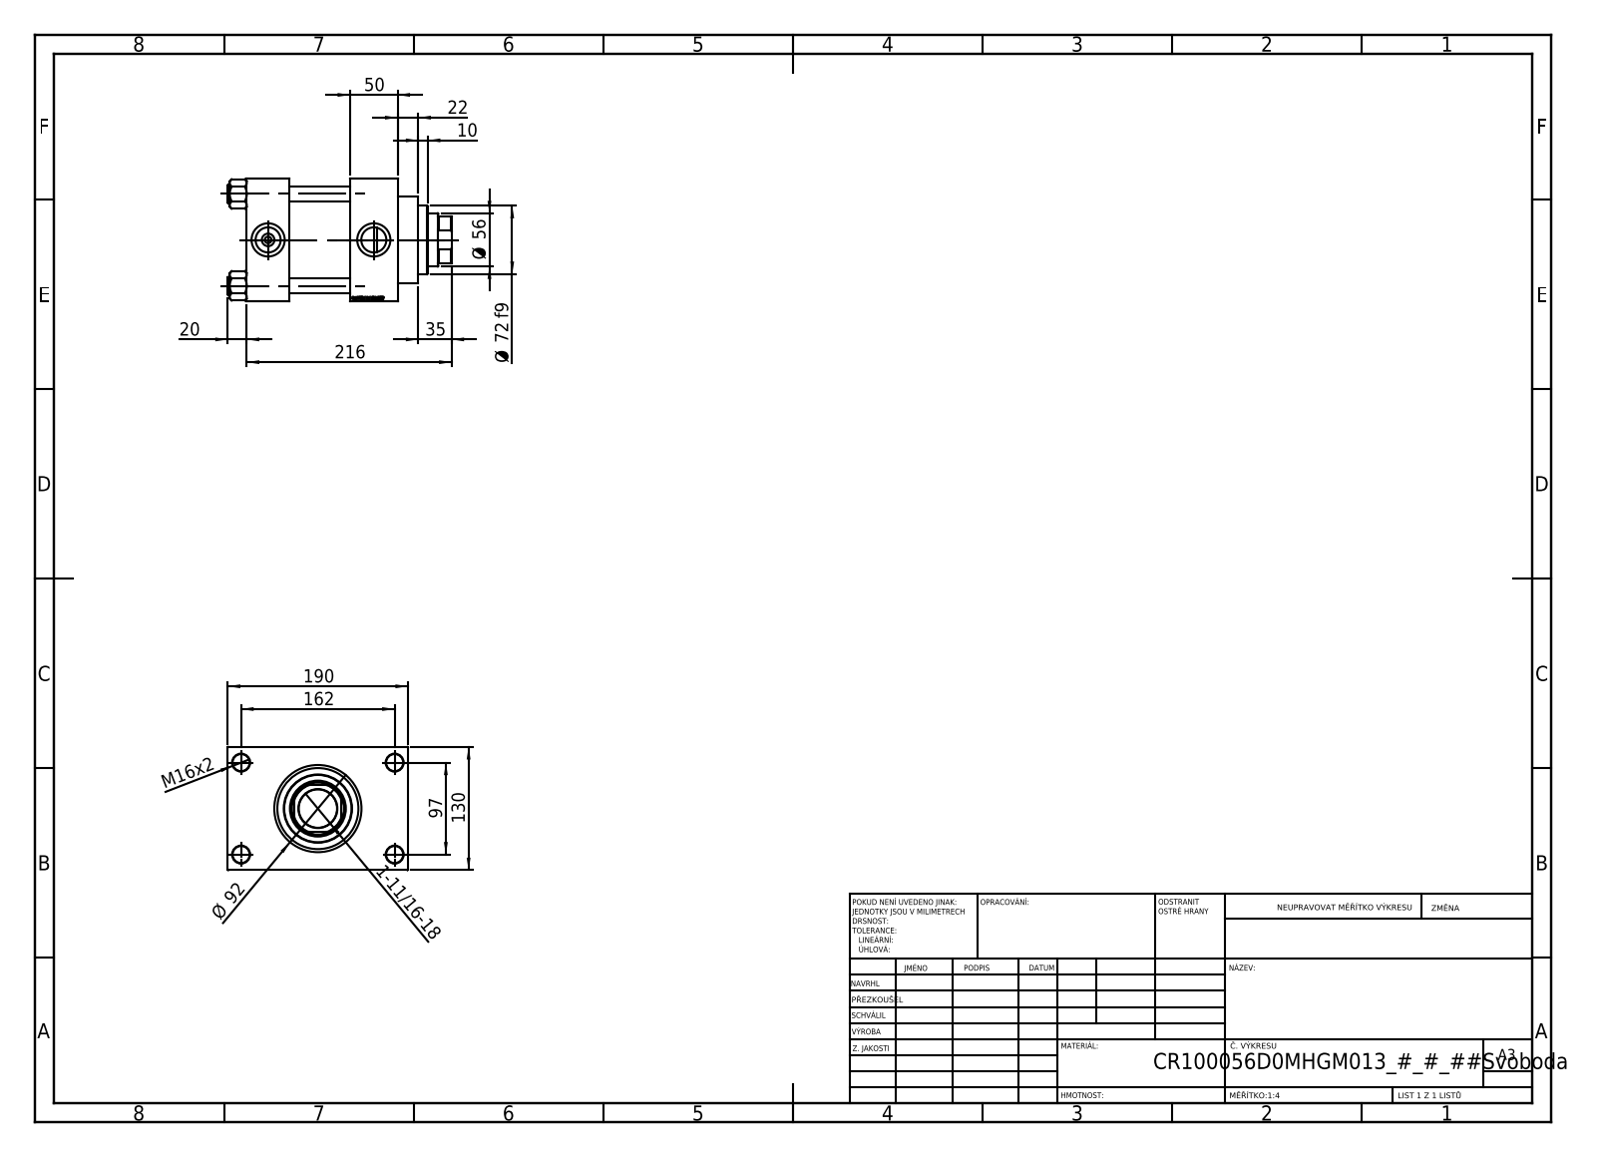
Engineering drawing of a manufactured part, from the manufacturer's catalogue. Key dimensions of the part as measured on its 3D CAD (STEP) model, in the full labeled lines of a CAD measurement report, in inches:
Part name (STEP PRODUCT): V215CR_VCP_D; V215CR_D_Body; V215CR_D_TYCINKA; NUT_M5_D (+1 more)
STEP written by: SolidWorks 2019 (CONFIG_CONTROL_DESIGN)
Units: inches
Bodies: 11 solids, 1151 faces (545 planar, 88 cylindrical, 518 other)
Overall size (bounding box): 9.291 × 7.48 × 5.118
Volume: 158.5 in³ · Surface area: 550.6 in²
Round holes (diameter × count): ⌀0.63 ×4, ⌀0.709 ×4, ⌀0.276 ×2, ⌀1.041 ×2, ⌀1.378 ×2, ⌀1.594 ×1, ⌀2.205 ×1, ⌀2.323 ×1, ⌀2.992 ×1, ⌀3.366 ×1, ⌀3.937 ×1
Round bosses / shafts (diameter × count): ⌀0.748 ×4, ⌀4.173 ×1, ⌀3.622 ×1, ⌀2.835 ×1
Partial cylindrical surfaces — rounded edges, fillets, slot ends (radius × count): R1.063 ×1
Main face-to-face distances: 5.118, 4.488, 1.969, 1.772, 4.291, 2.52, 6.26, 1.181, 6.299, 0.512
Hole centre spacings: 1.281, 2.698, 3.717, 3.815, 4.026, 5.096, 6.367, 3.819
